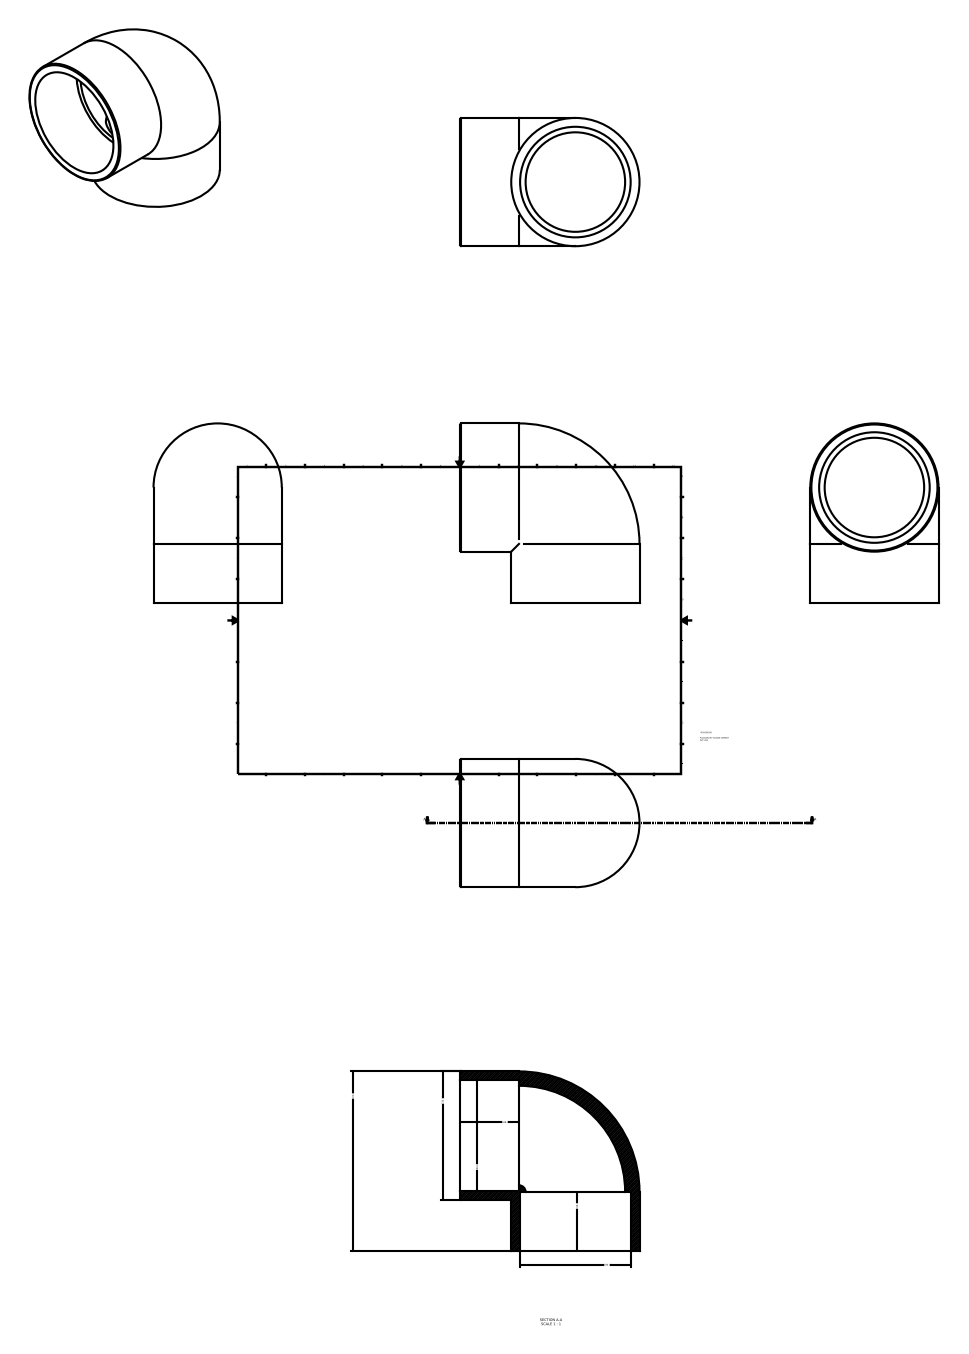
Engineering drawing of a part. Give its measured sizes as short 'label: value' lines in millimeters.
name: (_AS)050500200
written by: Autodesk Inventor 2015 (AUTOMOTIVE_DESIGN)
unit: mm
bodies: 1 solid, 11 faces (4 planar, 4 cylindrical, 3 other)
size: 324 × 324 × 232
volume: 5 061 000 mm³; area: 527 881 mm²
holes: 2× ⌀200
bosses: 2× ⌀232
face distances: 106
